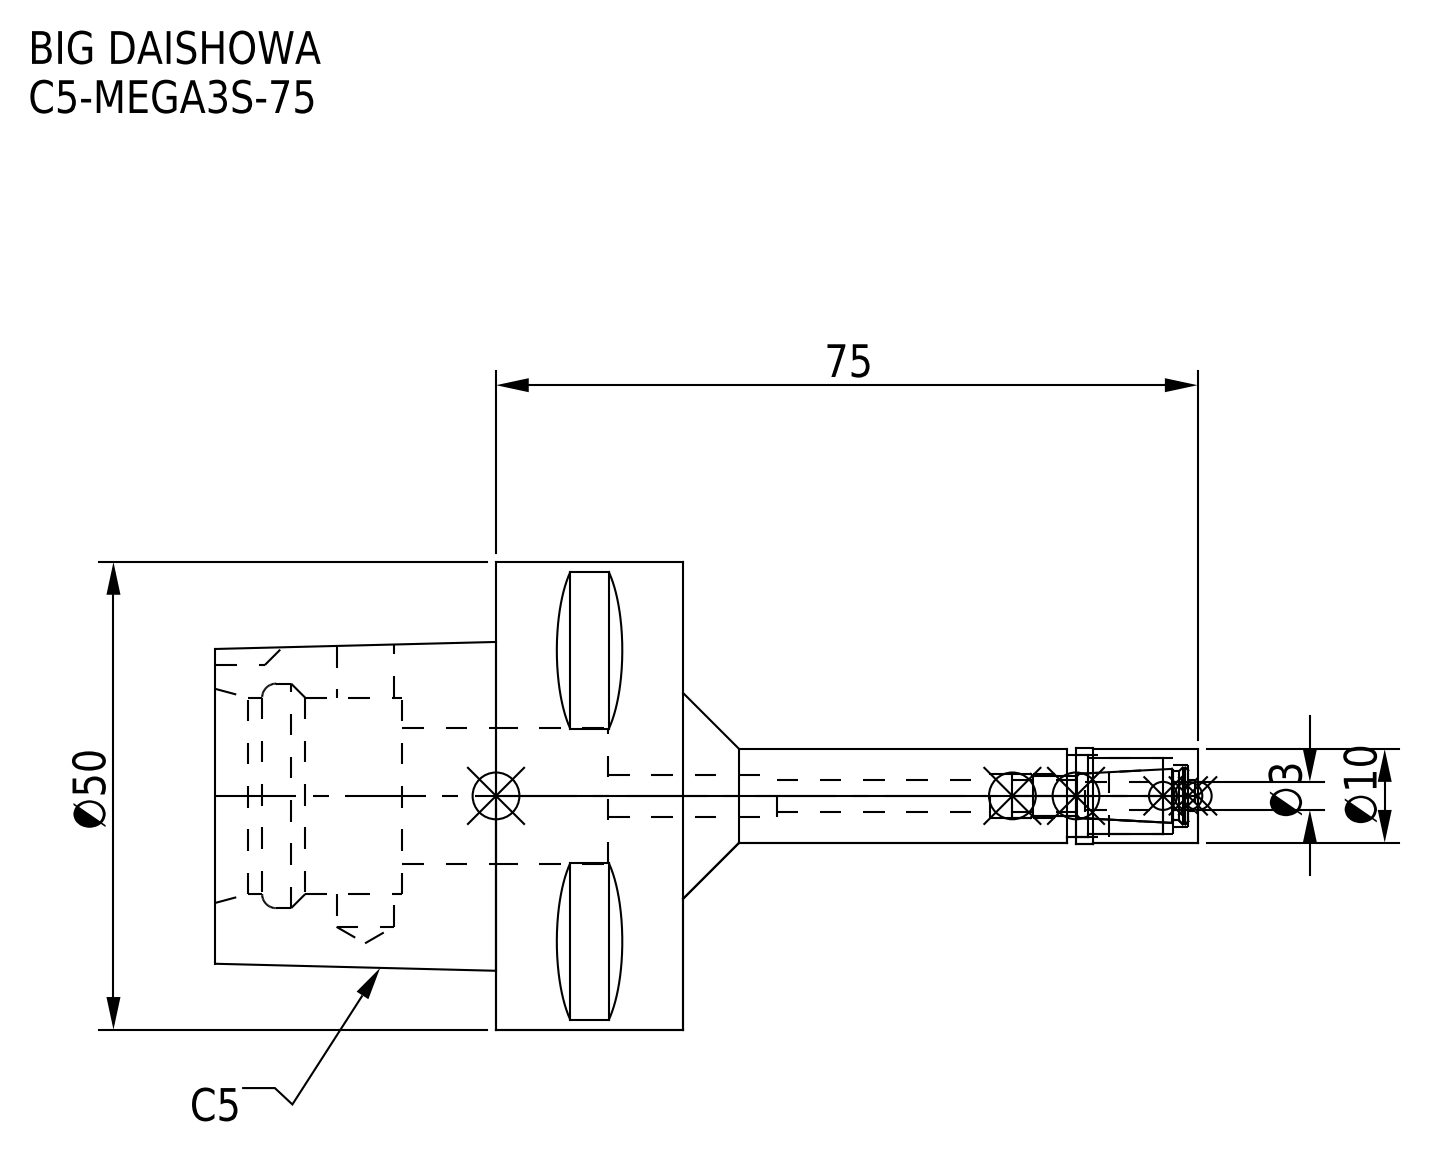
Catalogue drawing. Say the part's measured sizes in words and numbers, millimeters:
The part is named "C5-MEGA3S-75_1.stp; C5-MEGA3S-75-030_ASM.stp; C5-MEGA3S-75; C5-MEGA3S-75-030.stp (+3 more)". Its 3-D file was written by "SolidWorks 2019 (CONFIG_CONTROL_DESIGN)". It is 2 solids with 93 faces: 38 planar, 39 cylindrical and 16 other. Overall it measures 105 by 50 by 50 millimeters. Its volume is 58 607 cubic millimeters and its surface area 16 100 square millimeters. Round holes: 1 of diameter 3.3, 1 of diameter 3.4, 1 of diameter 4.5, 1 of diameter 4.7, 1 of diameter 6.1, 1 of diameter 6.6, 1 of diameter 8.2, 1 of diameter 8.7, 1 of diameter 14.5, 1 of diameter 21, 1 of diameter 24. Round bosses or shafts: 1 of diameter 50, 1 of diameter 10.3, 1 of diameter 10. Partial cylindrical surfaces (rounded edges, fillets, slot ends): 1 of radius 4. The main face-to-face distances are 20, 30, 50, 44, 10, 12, 42, 8, 19.18, 22.
